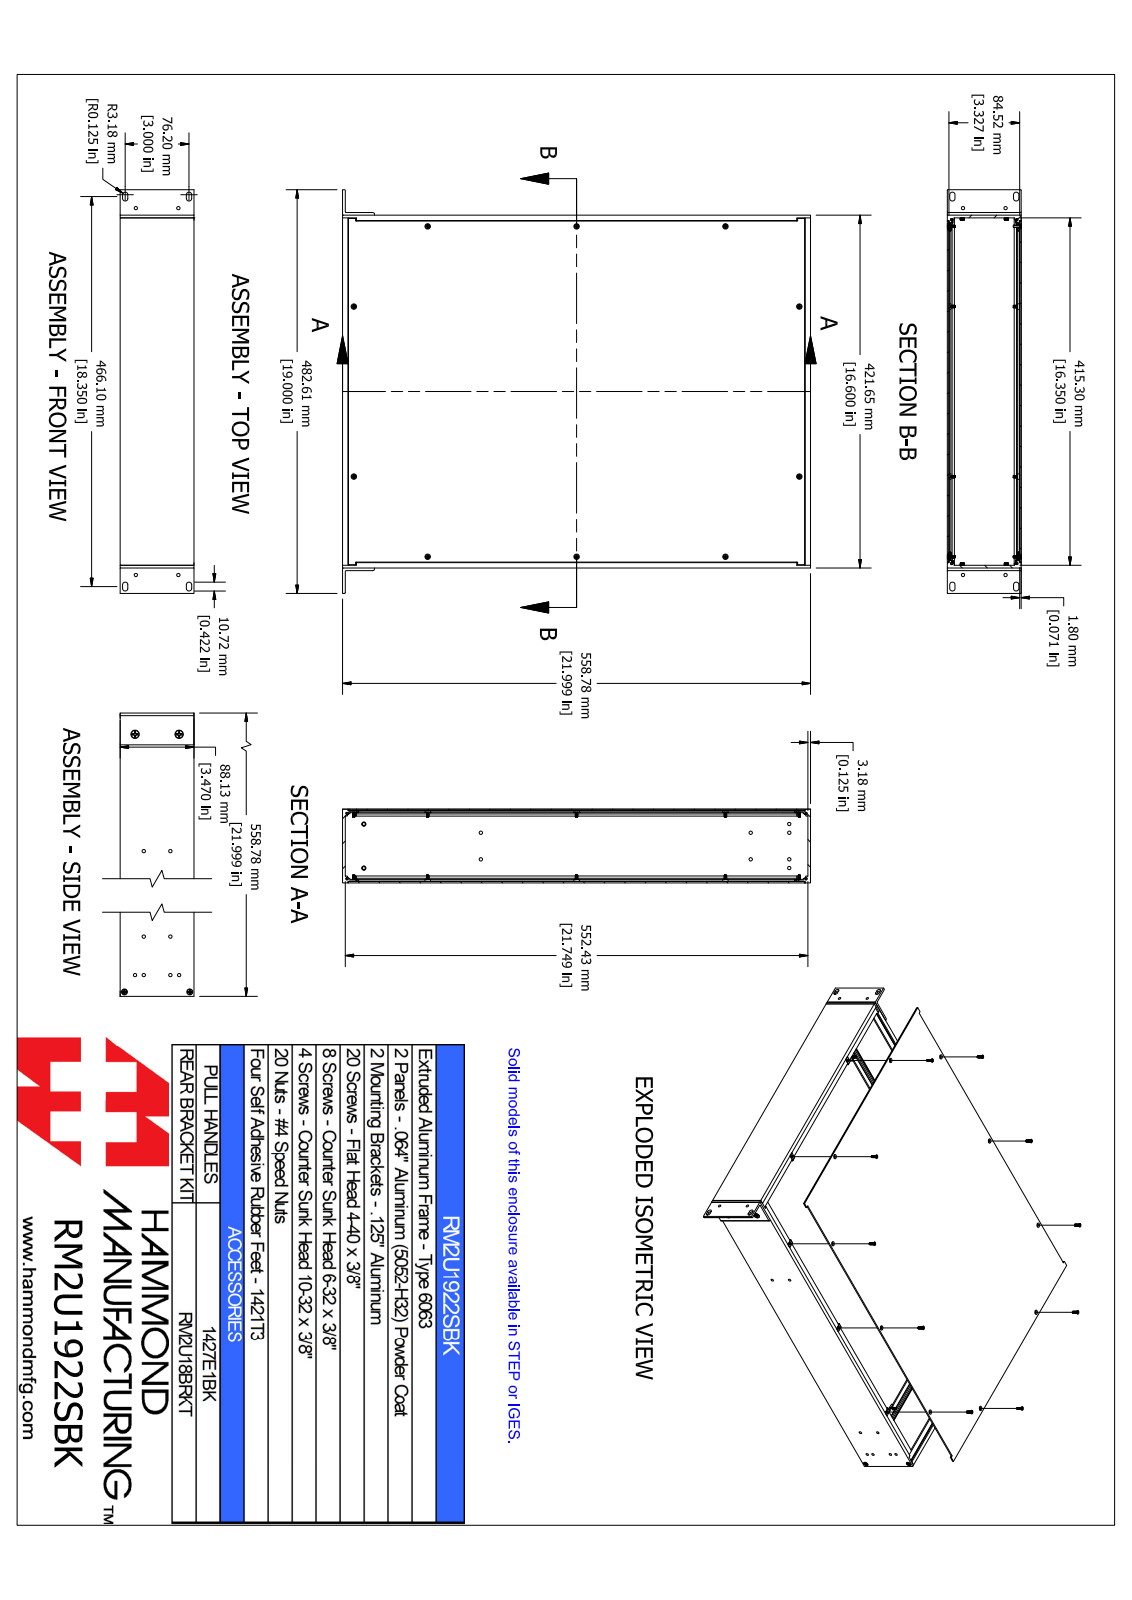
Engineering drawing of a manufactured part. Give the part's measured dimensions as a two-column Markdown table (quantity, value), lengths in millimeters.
| quantity | value |
| --- | --- |
| part name | RM2U1922SBK |
| STEP written by | SolidWorks 2021 (AUTOMOTIVE_DESIGN) |
| units | millimeters |
| bodies | 60 solids, 2284 faces (952 planar, 544 cylindrical, 788 other) |
| overall size | 558.8 × 482.6 × 88.2 |
| volume | 1 543 000 mm³ |
| surface area | 1 407 000 mm² |
| round holes (diameter × count) | 4 × 10, 4.1 × 10, 4 × 6, 4.2 × 6, 3.5 × 4, 4 × 4, 4 × 4, 4.3 × 4, 5 × 2 |
| round bosses / shafts (diameter × count) | 5.1 × 10, 2.8 × 10, 6 × 4, 3.5 × 4, 9.1 × 2, 4.8 × 2 |
| partial cylindrical surfaces (radius × count) | 0.3 × 80, 0.6 × 80, 0.2 × 40, 0.4 × 40, 0.4 × 16, 1 × 16, 1 × 14, 0.9 × 8 |
| main face-to-face distances | 1.8, 86.3, 88.1, 86.3, 1.8, 84.5, 418.5, 3.2, 3.2, 555.6 |
| hole center spacings | 177.8, 130.2, 433, 203.2, 282.7, 311.8, 355.6, 400.2 |
